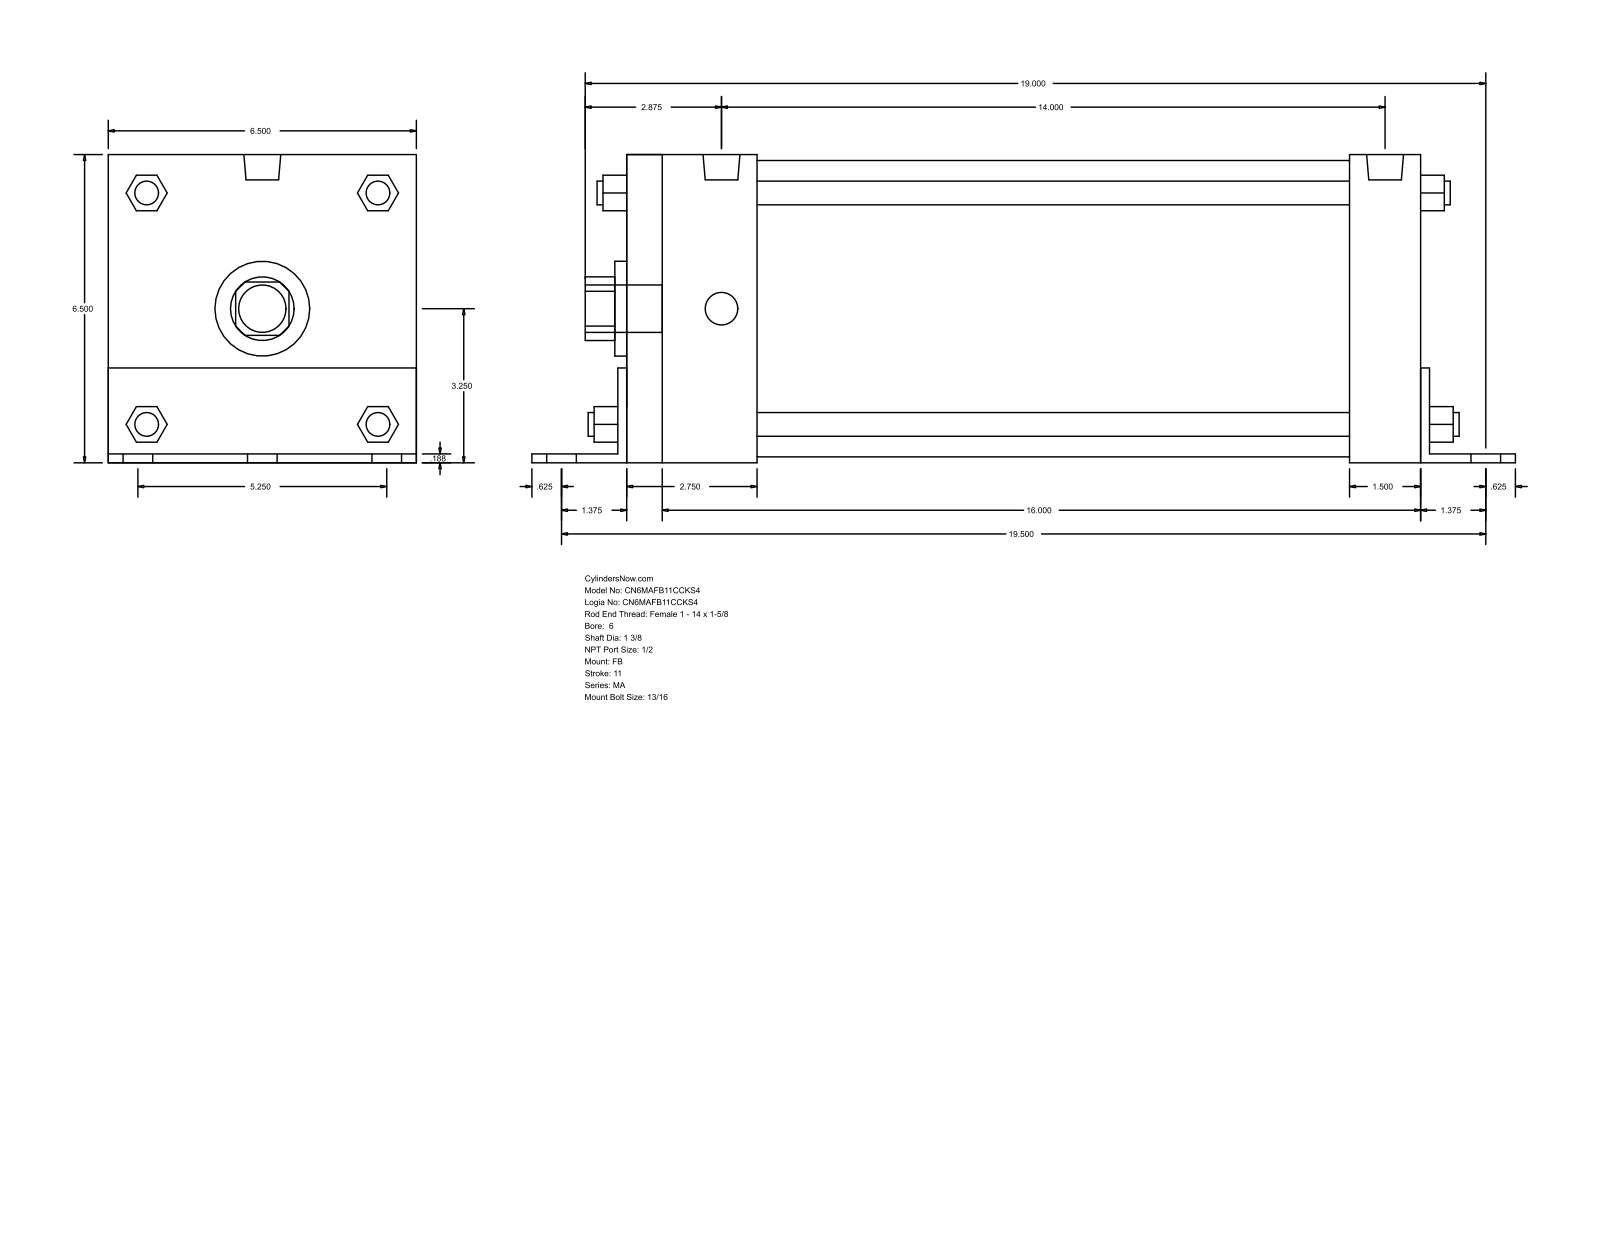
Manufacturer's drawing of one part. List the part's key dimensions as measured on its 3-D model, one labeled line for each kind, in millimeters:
Part name (STEP PRODUCT): MA_FB__0600_1.375
STEP written by: GSSL Pune (CONFIG_CONTROL_DESIGN)
Units: millimetres
Bodies: 0 solids, 140 faces (105 planar, 35 cylindrical, 0 other)
Overall size (bounding box): 523.88 × 165.15 × 165.1
Round holes (diameter × count): ⌀34.92 ×1, ⌀50.8 ×1, ⌀158.75 ×1
Round bosses / shafts (diameter × count): ⌀20.64 ×6, ⌀17.46 ×4, ⌀12.7 ×4, ⌀19.77 ×2, ⌀25.4 ×1
Partial cylindrical surfaces — rounded edges, fillets, slot ends (radius × count): R17.06 ×1, R32.05 ×1
Main face-to-face distances: 165.1, 4.76, 422.27, 165.15, 4.71, 160.39, 4.77, 38.1, 427.04, 431.8
